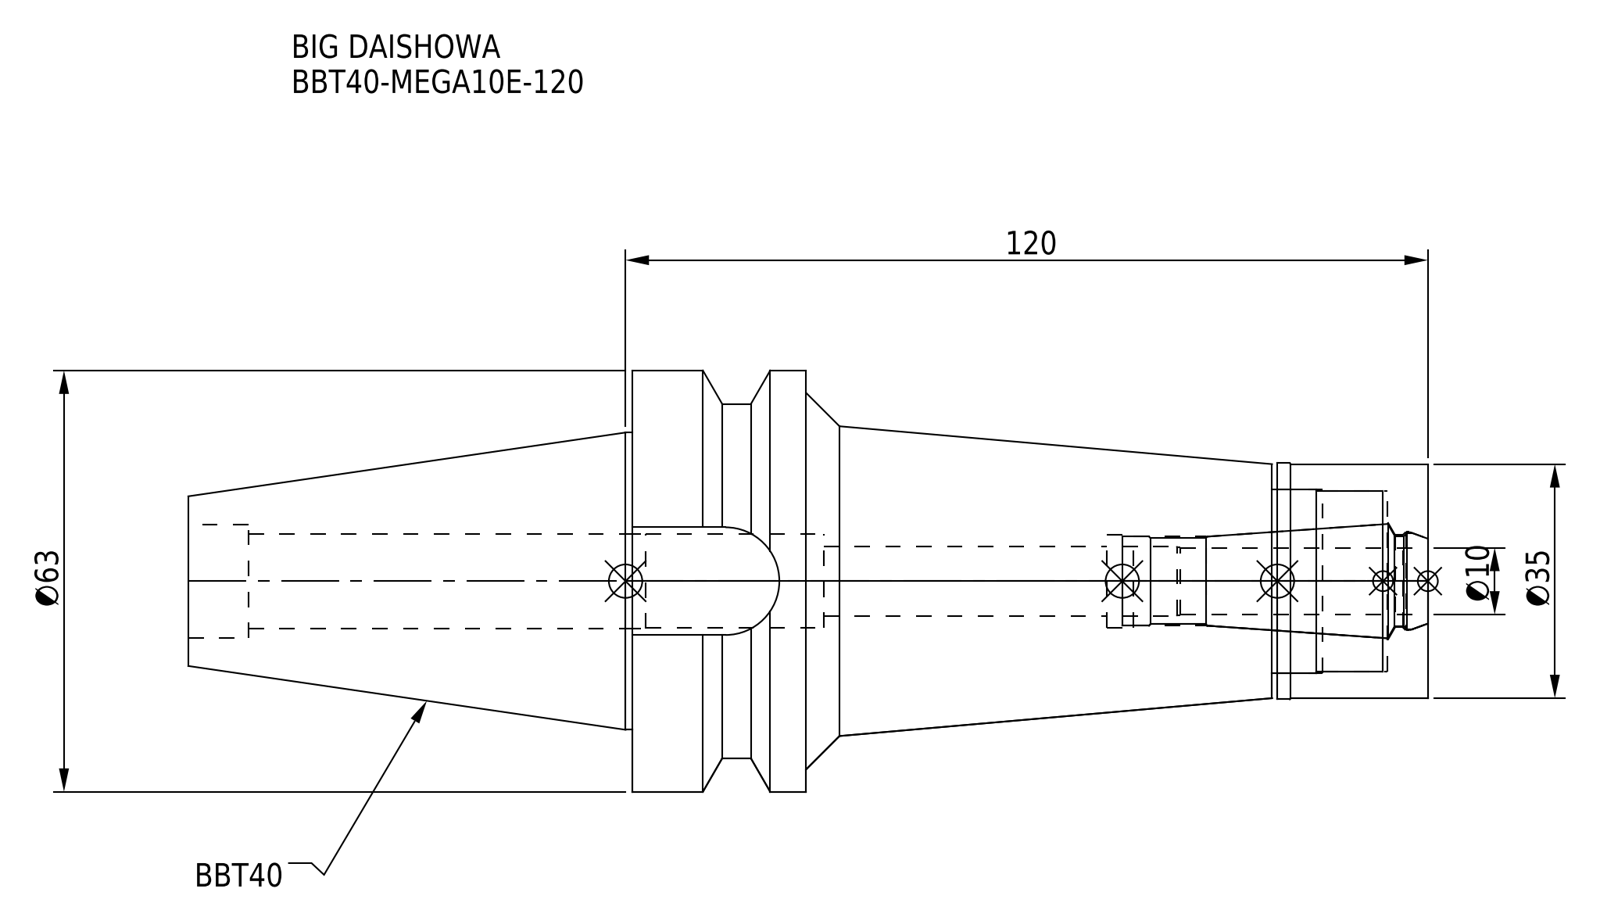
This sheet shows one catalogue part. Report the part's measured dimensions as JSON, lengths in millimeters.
{"part_name": "BBT40-MEGA10E-120; MEN10_1.stp; BBT40-MEGA10E-120-100-FreeParts; DXF_TEMP_ASSY_ASM_4_ASM.stp (+3 more)", "step_written_by": "SolidWorks 2019 (CONFIG_CONTROL_DESIGN)", "units": "millimeters", "bodies": {"solids": 2, "faces": 81, "planar": 21, "cylindrical": 40, "other": 20}, "overall_size": [185.4, 63, 63], "volume_mm3": 225232, "surface_area_mm2": 41283, "round_holes": [[10.4, 1], [13.3, 1], [13.8, 1], [13.9, 1], [14, 1], [14.2, 1], [14.7, 1], [17, 1], [27, 1], [27.5, 1]], "round_bosses_or_shafts": [[63, 1], [53, 1], [44.45, 1], [35.3, 1], [35, 1]], "partial_cylinders_radius": [[8.05, 1]], "face_to_face_distances": [119, 93, 26, 45, 22.5, 70.5, 96.5, 23.3, 0.8, 69.7]}
